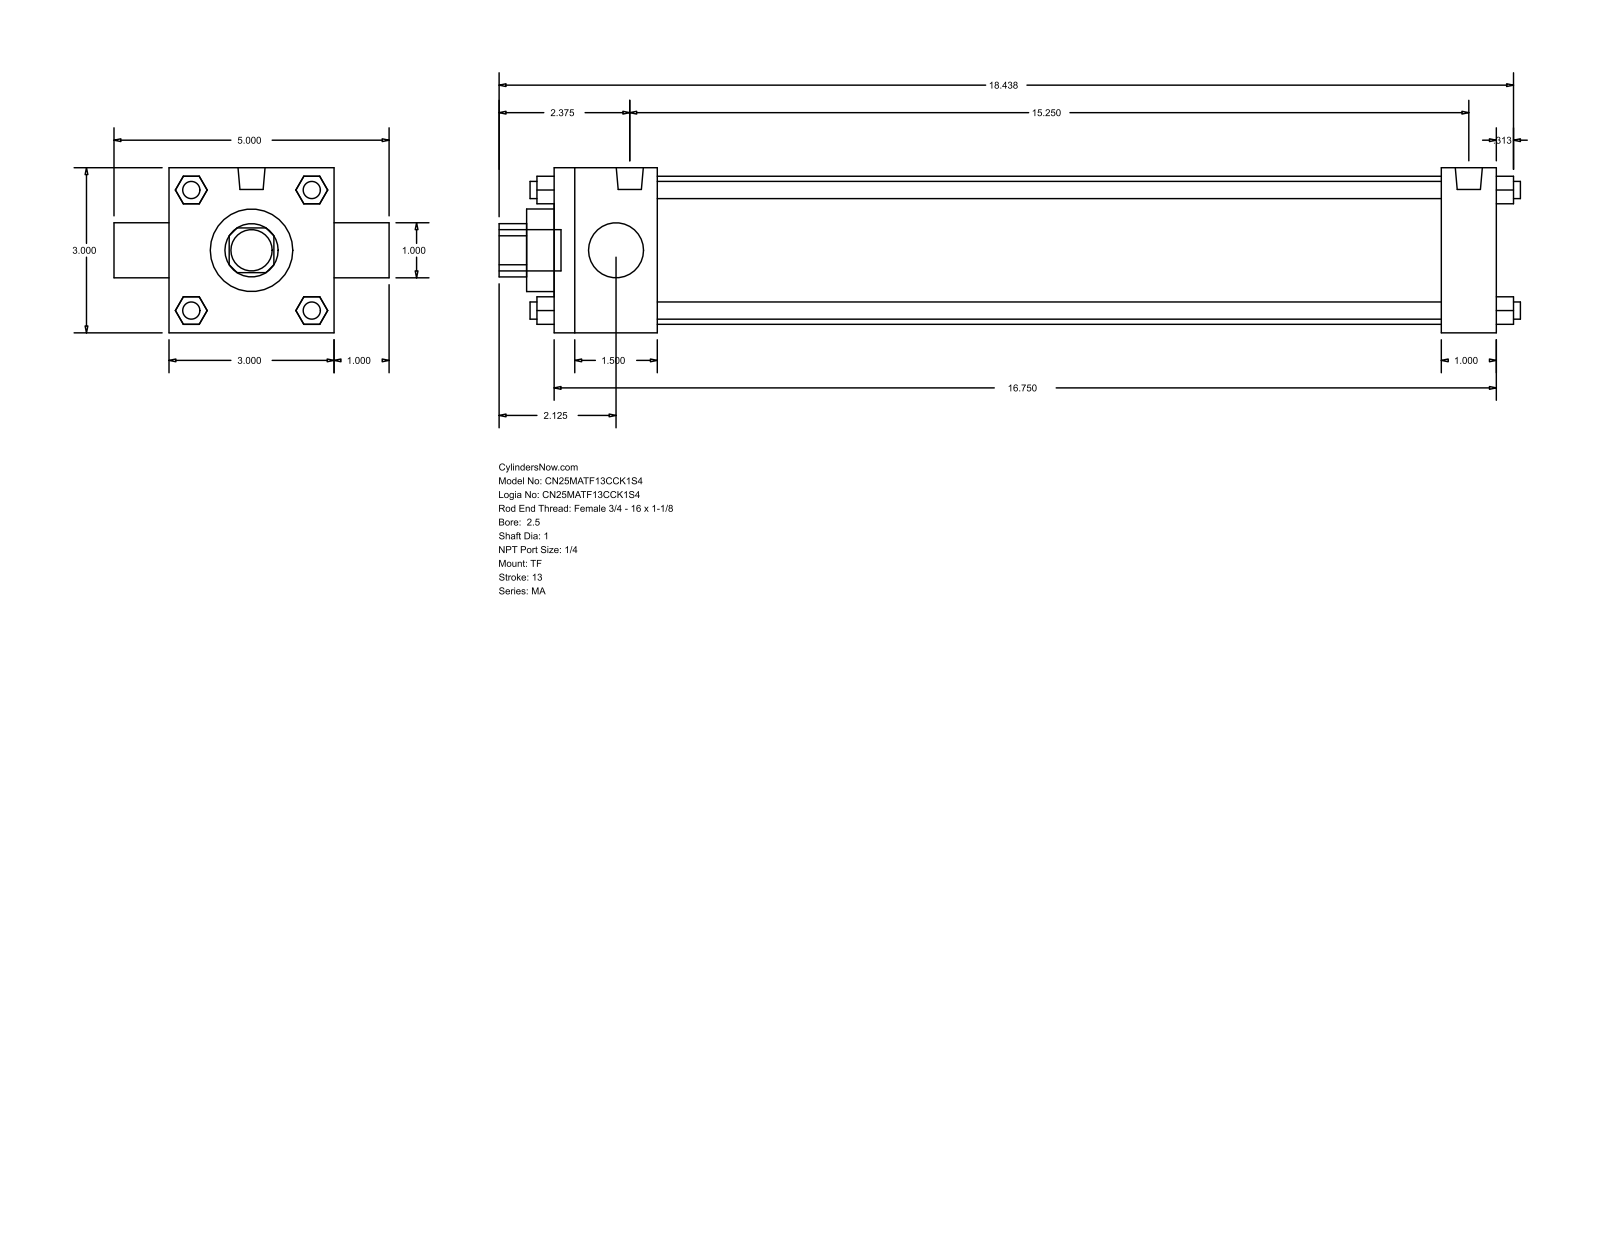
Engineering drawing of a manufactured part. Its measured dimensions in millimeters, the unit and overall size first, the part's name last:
Units: millimetres
Overall size (bounding box): 471.49 × 127 × 76.2
Round holes (diameter × count): ⌀25.4 ×2, ⌀38.1 ×1, ⌀68.33 ×1
Round bosses / shafts (diameter × count): ⌀7.94 ×7, ⌀12.49 ×2, ⌀19.05 ×1
Partial cylindrical surfaces — rounded edges, fillets, slot ends (radius × count): R12.29 ×1
Main face-to-face distances: 76.2, 434.98, 25.4, 12.7, 47.63, 409.58, 361.95, 387.35, 101.6, 27.81
Bodies: 0 solids, 120 faces (92 planar, 28 cylindrical, 0 other)
Part name (STEP PRODUCT): MA_TF__0250_1
STEP written by: GSSL Pune (CONFIG_CONTROL_DESIGN)
